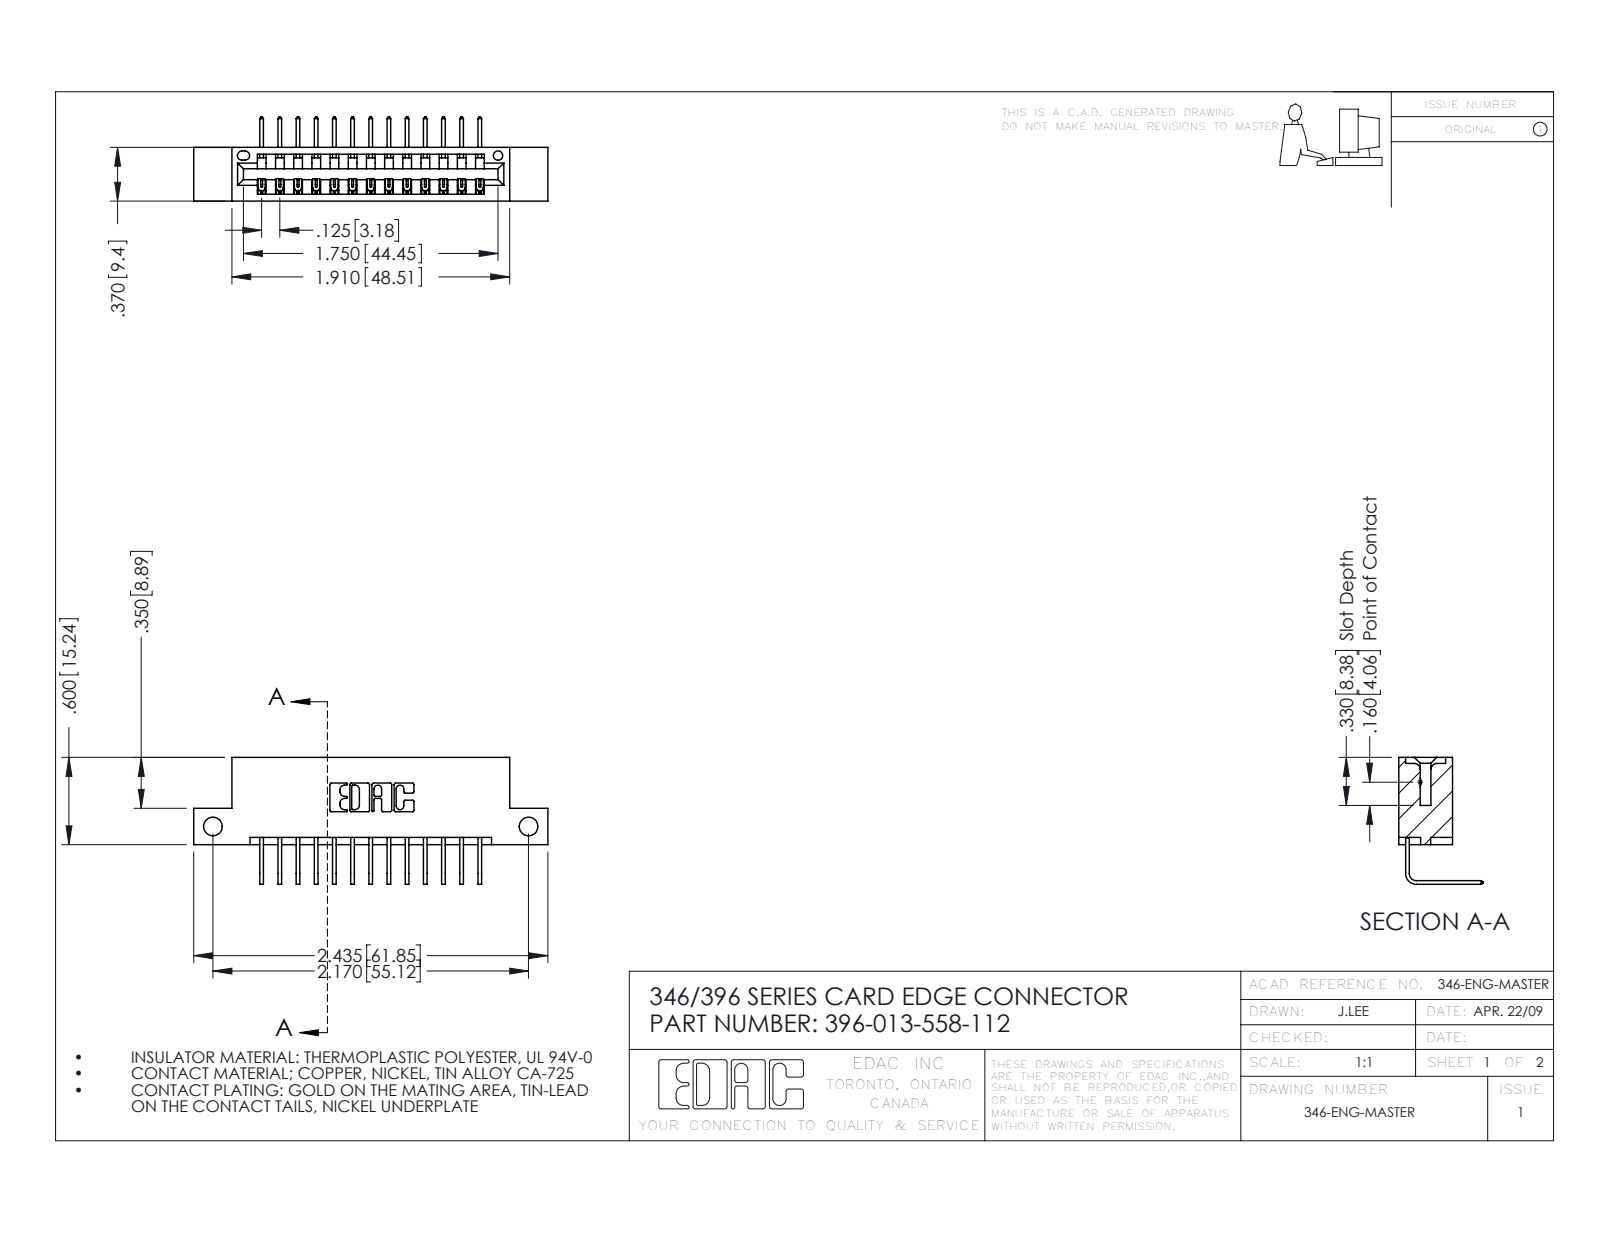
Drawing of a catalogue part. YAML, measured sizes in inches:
part_name: "346 Part_Flush Mounting Lugs - Side Mount; 396-013-558-112; 345-292-001_558 Tail - 2"
step_written_by: "SolidWorks 2016 (CONFIG_CONTROL_DESIGN)"
units: inches
bodies: {solids: 14, faces: 902, planar: 622, cylindrical: 280, other: 0}
overall_size: [2.435, 0.873, 0.58]
volume: 0.346
surface_area: 10.69
round_holes:
  - {diameter: 0.128, count: 2}
  - {diameter: 0.064, count: 1}
partial_cylinders:
  - {radius: 0.006, count: 26}
  - {radius: 0.01, count: 22}
  - {radius: 0.007, count: 6}
  - {radius: 0.031, count: 6}
  - {radius: 0.026, count: 3}
  - {radius: 0.031, count: 2}
  - {radius: 0.04, count: 2}
  - {radius: 0.014, count: 1}
face_to_face_distances: [0.25, 0.322, 0.048, 0.37, 0.298, 0.025, 0.072, 0.148, 0.222, 0.1]
hole_center_spacings: [2.17]
